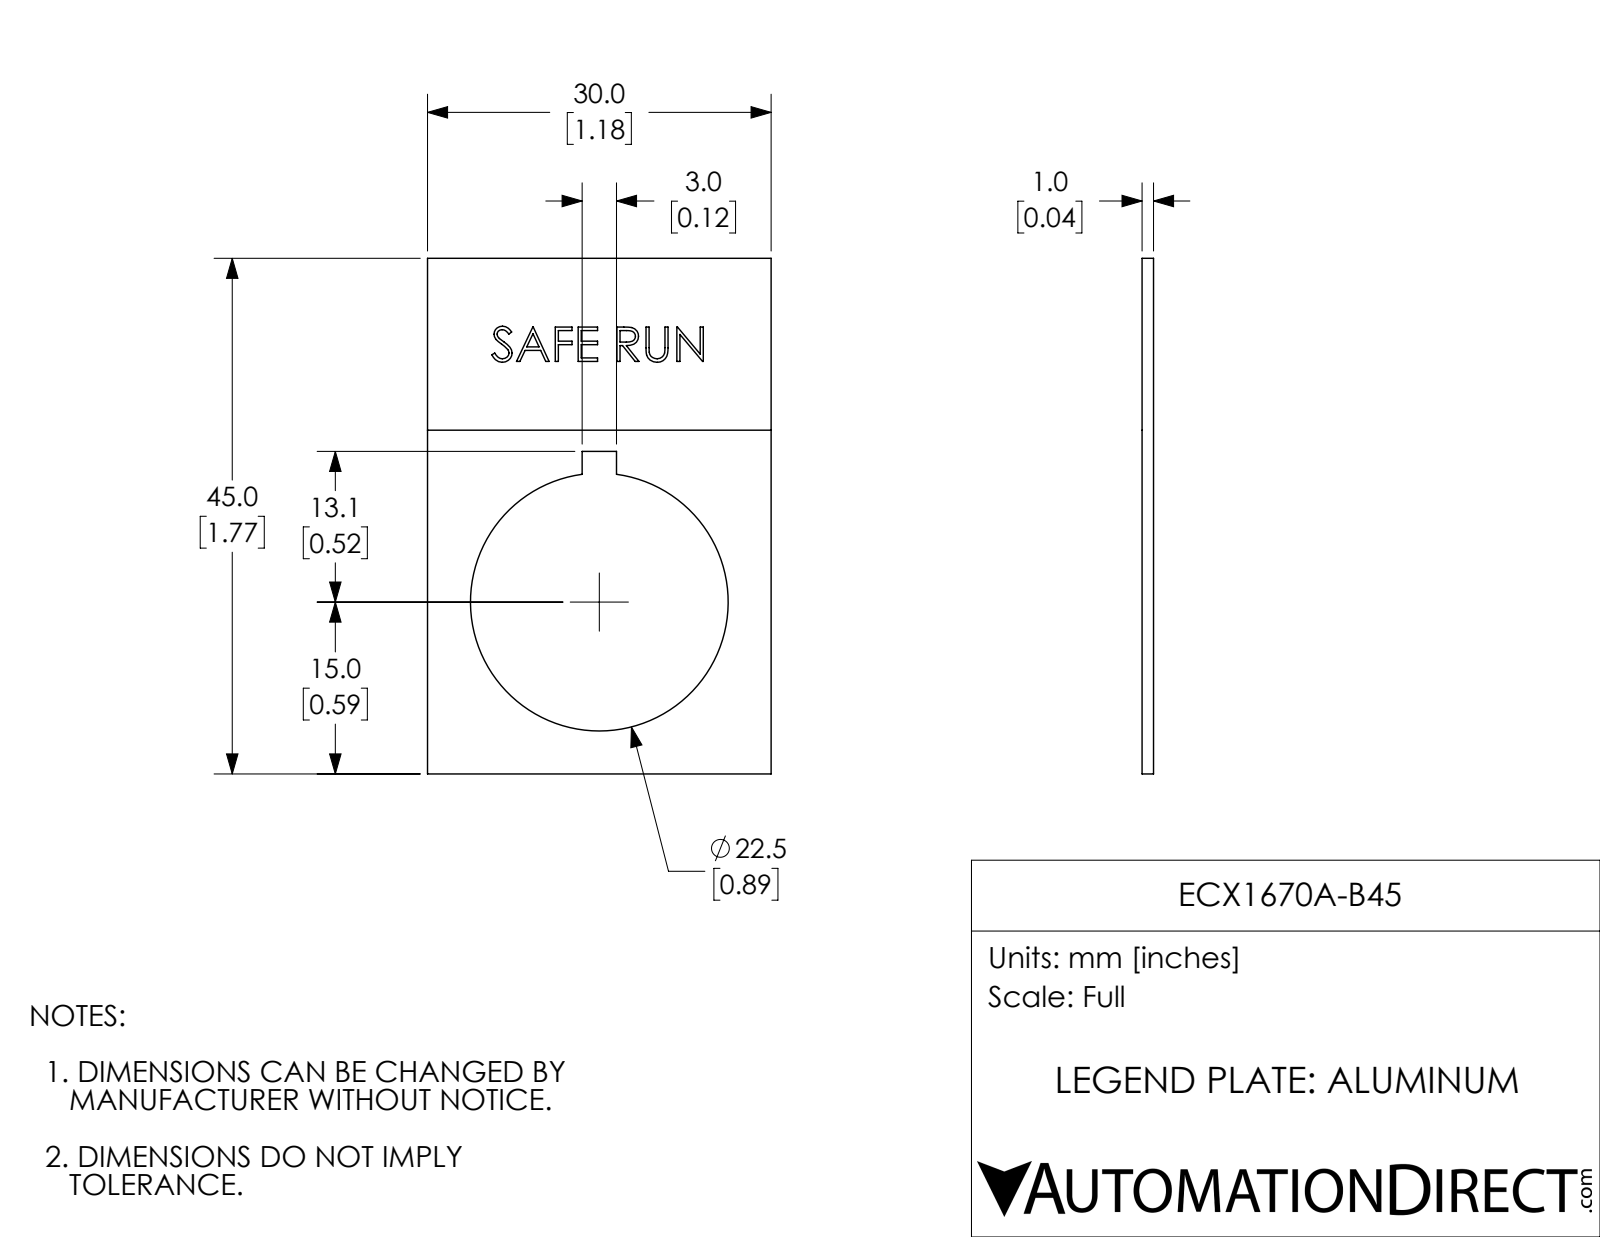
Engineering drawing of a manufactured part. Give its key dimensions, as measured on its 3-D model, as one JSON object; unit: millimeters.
{"part_name": "ECX1670A-B45", "step_written_by": "SolidWorks 2017 (AUTOMOTIVE_DESIGN)", "units": "millimeters", "bodies": {"solids": 1, "faces": 111, "planar": 81, "cylindrical": 3, "other": 27}, "overall_size": [45, 30, 1], "volume_mm3": 950, "surface_area_mm2": 2121, "round_holes": [[22.5, 1]], "face_to_face_distances": [1, 30, 45, 1, 13.5, 16.5, 16.8, 28.1, 3, 0.3]}
